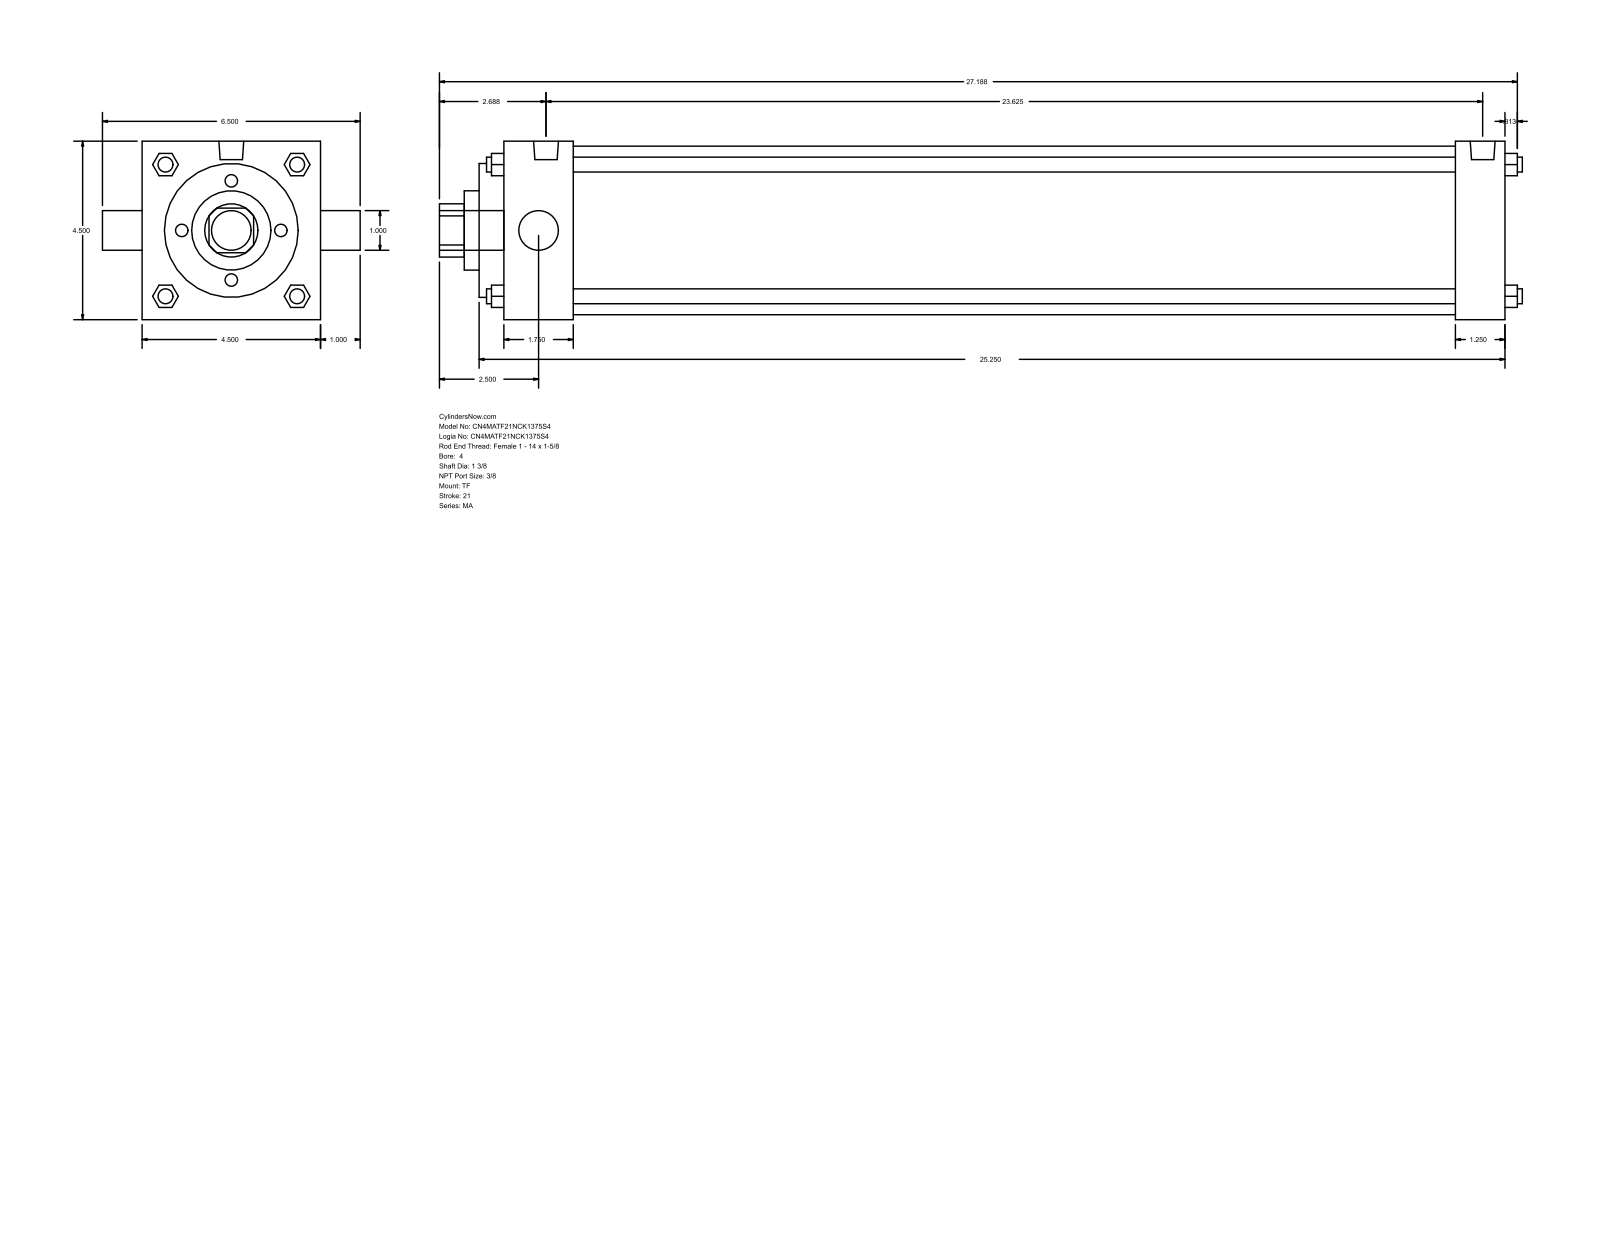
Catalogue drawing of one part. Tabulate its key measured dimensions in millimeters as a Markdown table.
| quantity | value |
| --- | --- |
| part name | MA_TF__0400_1.375 |
| STEP written by | GSSL Pune (CONFIG_CONTROL_DESIGN) |
| units | millimeters |
| bodies | 0 solids, 122 faces (93 planar, 29 cylindrical, 0 other) |
| overall size | 693.74 × 165.1 × 114.3 |
| round holes (diameter × count) | 25.4 × 1, 34.92 × 1, 50.8 × 1, 85.72 × 1, 107.95 × 1 |
| round bosses / shafts (diameter × count) | 9.53 × 4, 11.11 × 3, 15.93 × 2, 25.4 × 1 |
| partial cylindrical surfaces (radius × count) | 17.06 × 1 |
| main face-to-face distances | 114.3, 641.35, 657.22, 15.87, 625.48, 609.61, 31.74, 60.32, 44.45, 565.16 |
